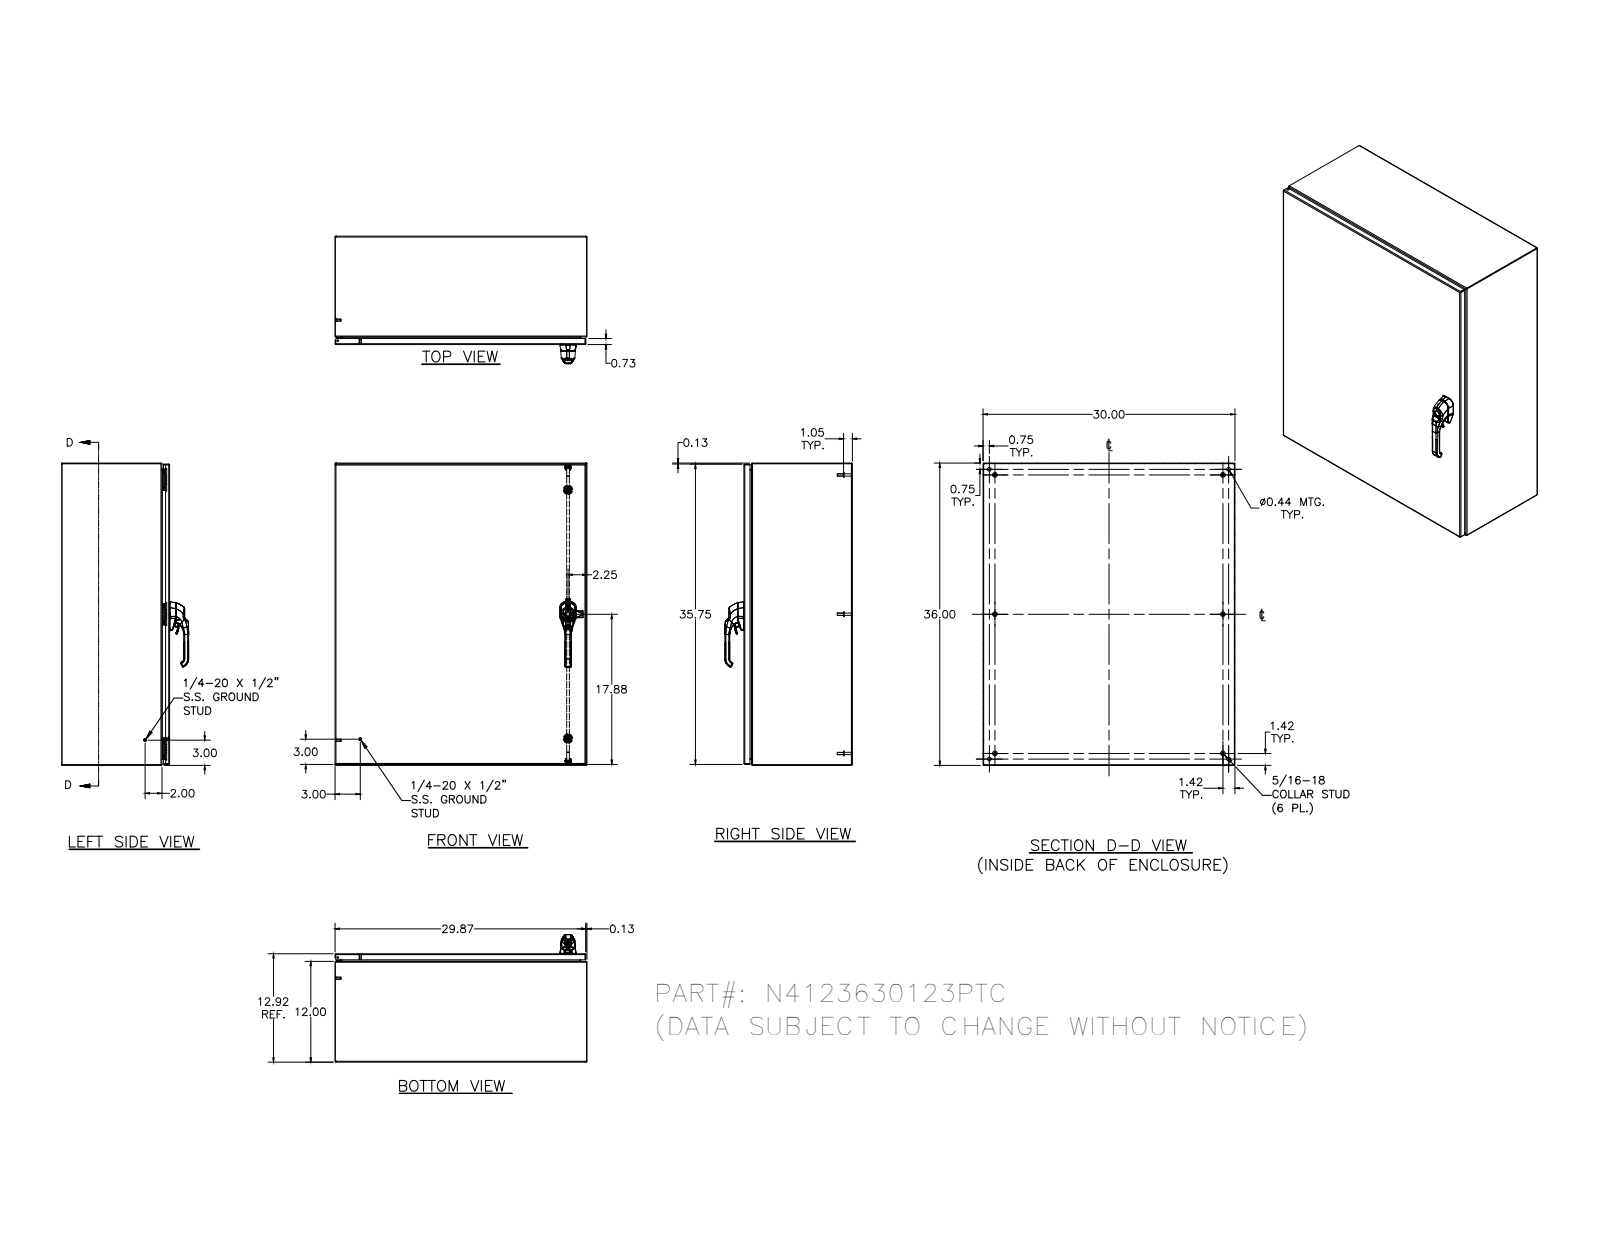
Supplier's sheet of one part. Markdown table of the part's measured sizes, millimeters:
| quantity | value |
| --- | --- |
| part name | N4123630123PTC; N4123630123PTCBKP; N41236303PTCLID; HFW328176 (+8 more) |
| STEP written by | Autodesk Inventor 2011 (AUTOMOTIVE_DESIGN) |
| units | millimeters |
| bodies | 60 solids, 3398 faces (1066 planar, 1279 cylindrical, 1053 other) |
| overall size | 914.4 × 762 × 385.7 |
| volume | 4 926 000 mm³ |
| surface area | 5 293 000 mm² |
| round holes (diameter × count) | 4.8 × 7, 2.4 × 6, 3.9 × 6, 4.2 × 6, 4.4 × 6, 4.2 × 4, 5 × 4, 11.1 × 4, 4 × 3, 5.4 × 3, 6 × 3, 9 × 3 |
| round bosses / shafts (diameter × count) | 6.4 × 14, 14.3 × 6, 9.1 × 6, 8.1 × 6, 7.6 × 6, 7 × 6, 6.5 × 6, 4.2 × 6 |
| partial cylindrical surfaces (radius × count) | 0.5 × 195, 0.3 × 79, 1.3 × 38, 0.8 × 34, 3 × 33, 0.4 × 26, 0.5 × 22, 3.2 × 21 |
| main face-to-face distances | 1.9, 326.2, 324.3, 328.1, 760.1, 912.5, 758.2, 762, 914.4, 910.6 |
| hole center spacings | 406.4, 406.3, 406.6, 812.7, 0.4, 16.8, 696.4, 406.5 |
